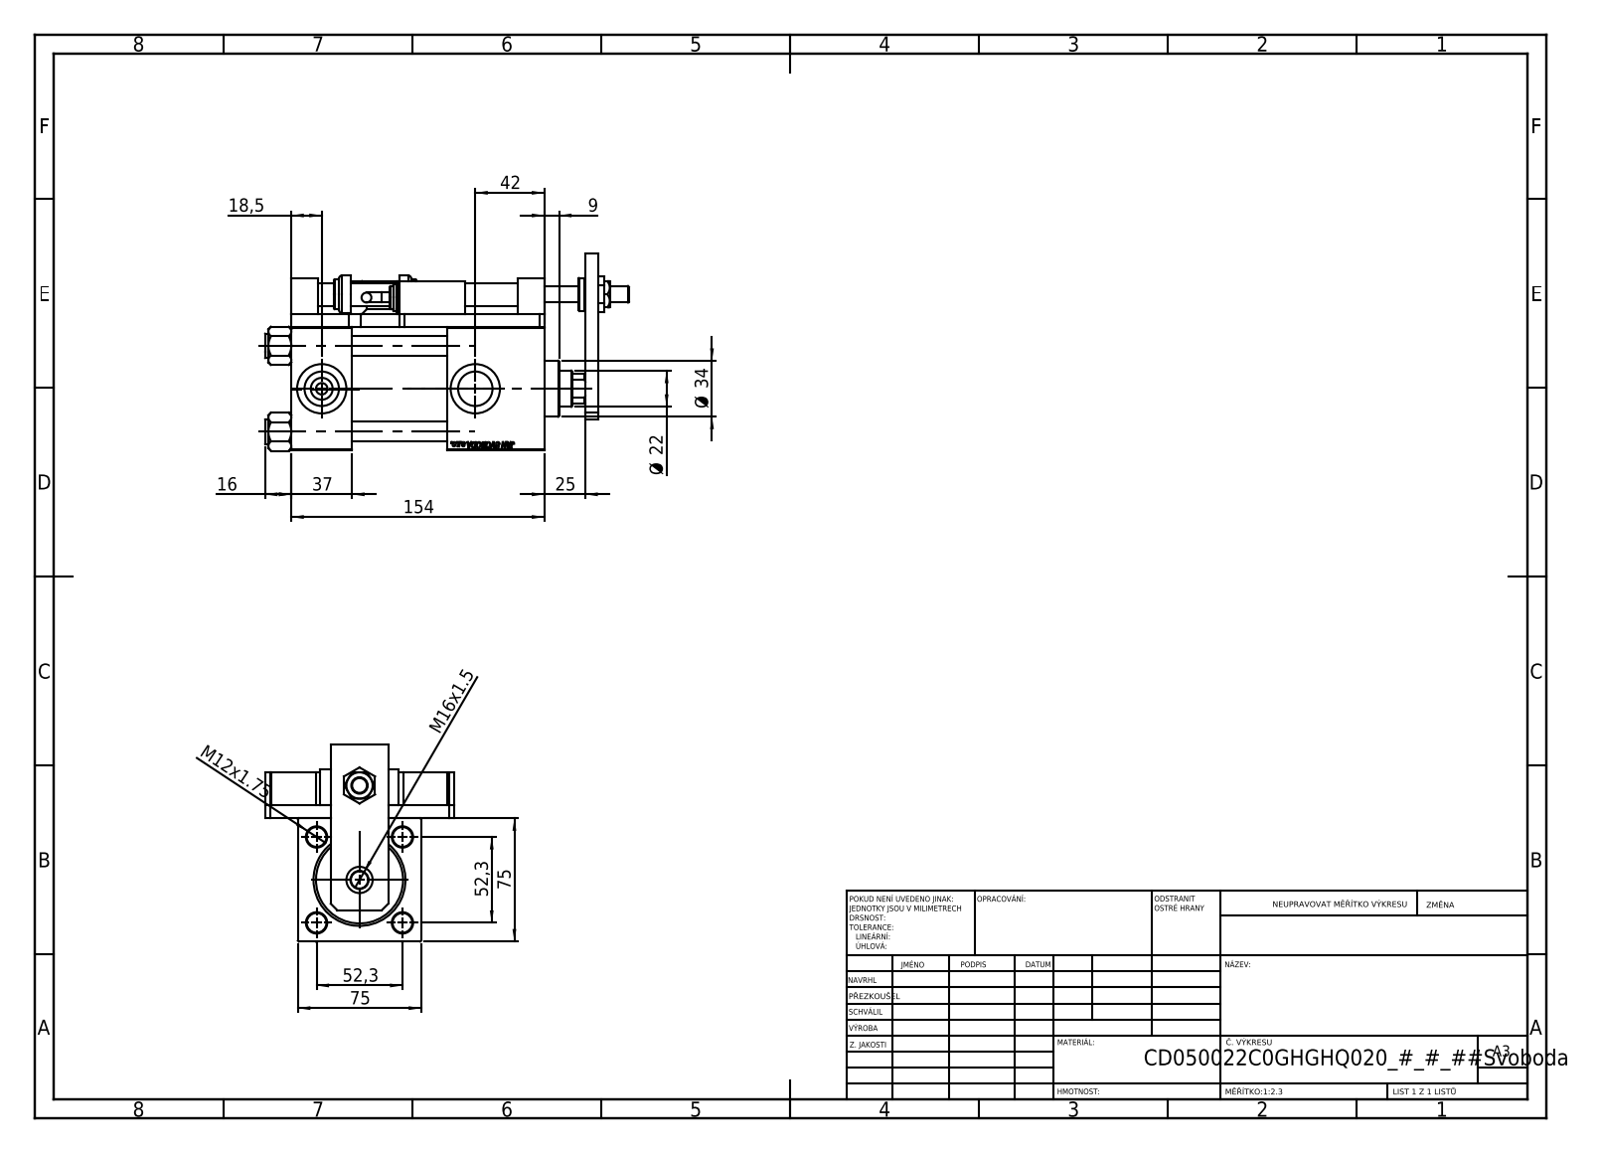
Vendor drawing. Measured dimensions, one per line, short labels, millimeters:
name: V215CD_SWITCH_Q_MAGNET; V215CD_VCP_C; V215CD_SWITCH_Q_ZARAZKA; V215CD_SWITCH_Q_PODLOZKA_BACK (+7 more)
written by: SolidWorks 2019 (CONFIG_CONTROL_DESIGN)
unit: mm
bodies: 24 solids, 1376 faces (647 planar, 154 cylindrical, 575 other)
size: 221.5 × 120.27 × 115
volume: 915 014 mm³; area: 230 269 mm²
holes: 4× ⌀8.5, 4× ⌀12, 4× ⌀13.5, 2× ⌀7, 2× ⌀20.96, 2× ⌀30, 1× ⌀10, 1× ⌀10.5, 1× ⌀14, 1× ⌀16, 1× ⌀22, 1× ⌀25
bosses: 4× ⌀15, 3× ⌀20, 2× ⌀16, 2× ⌀14, 2× ⌀6, 1× ⌀56, 1× ⌀34, 1× ⌀23
rounds: 4× R7.5, 1× R10.5
face distances: 8, 75, 20, 37, 83, 95, 154, 117, 92, 59
hole spacings: 36.98, 52.3, 32, 40.82, 73.96, 87.64, 138, 141.66
